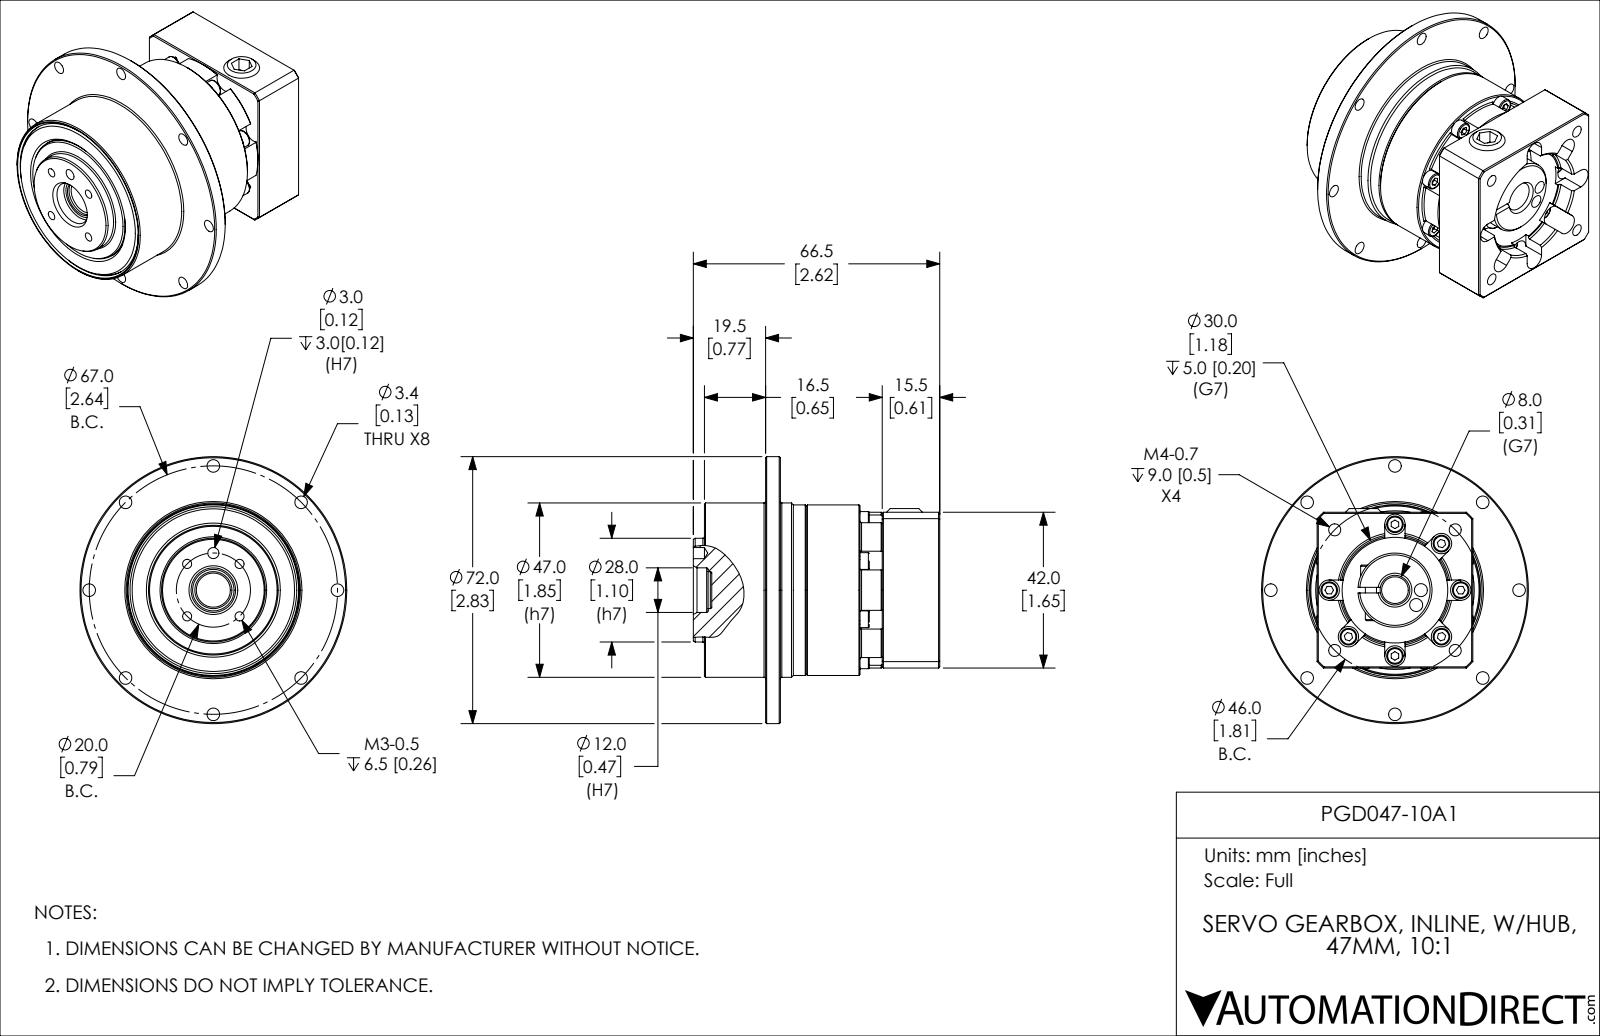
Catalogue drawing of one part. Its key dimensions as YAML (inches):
part_name: "PGD047-10A1"
step_written_by: "SolidWorks 2015 (AUTOMOTIVE_DESIGN)"
units: inches
bodies: {solids: 6, faces: 498, planar: 278, cylindrical: 147, other: 73}
overall_size: [2.835, 2.835, 2.618]
volume: 6.509
surface_area: 50
round_holes:
  - {diameter: 0.134, count: 8}
  - {diameter: 0.217, count: 8}
  - {diameter: 0.097, count: 4}
  - {diameter: 0.128, count: 4}
  - {diameter: 0.138, count: 2}
  - {diameter: 0.118, count: 1}
  - {diameter: 0.193, count: 1}
  - {diameter: 0.263, count: 1}
  - {diameter: 0.315, count: 1}
  - {diameter: 0.362, count: 1}
  - {diameter: 0.441, count: 1}
  - {diameter: 1.122, count: 1}
round_bosses_or_shafts:
  - {diameter: 0.177, count: 9}
  - {diameter: 0.157, count: 7}
  - {diameter: 2.835, count: 1}
  - {diameter: 1.85, count: 1}
  - {diameter: 1.811, count: 1}
  - {diameter: 1.102, count: 1}
  - {diameter: 0.787, count: 1}
  - {diameter: 0.748, count: 1}
partial_cylinders:
  - {radius: 0.108, count: 8}
  - {radius: 0.128, count: 1}
  - {radius: 0.827, count: 1}
  - {radius: 1.122, count: 1}
face_to_face_distances: [0.138, 0.433, 0.157, 0.276, 0.295, 0.945, 0.807, 1.083, 1.654, 0.65]
hole_center_spacings: [0.961, 1.493, 1.879, 1.016, 1.077, 1.376, 0.504, 0.62]
